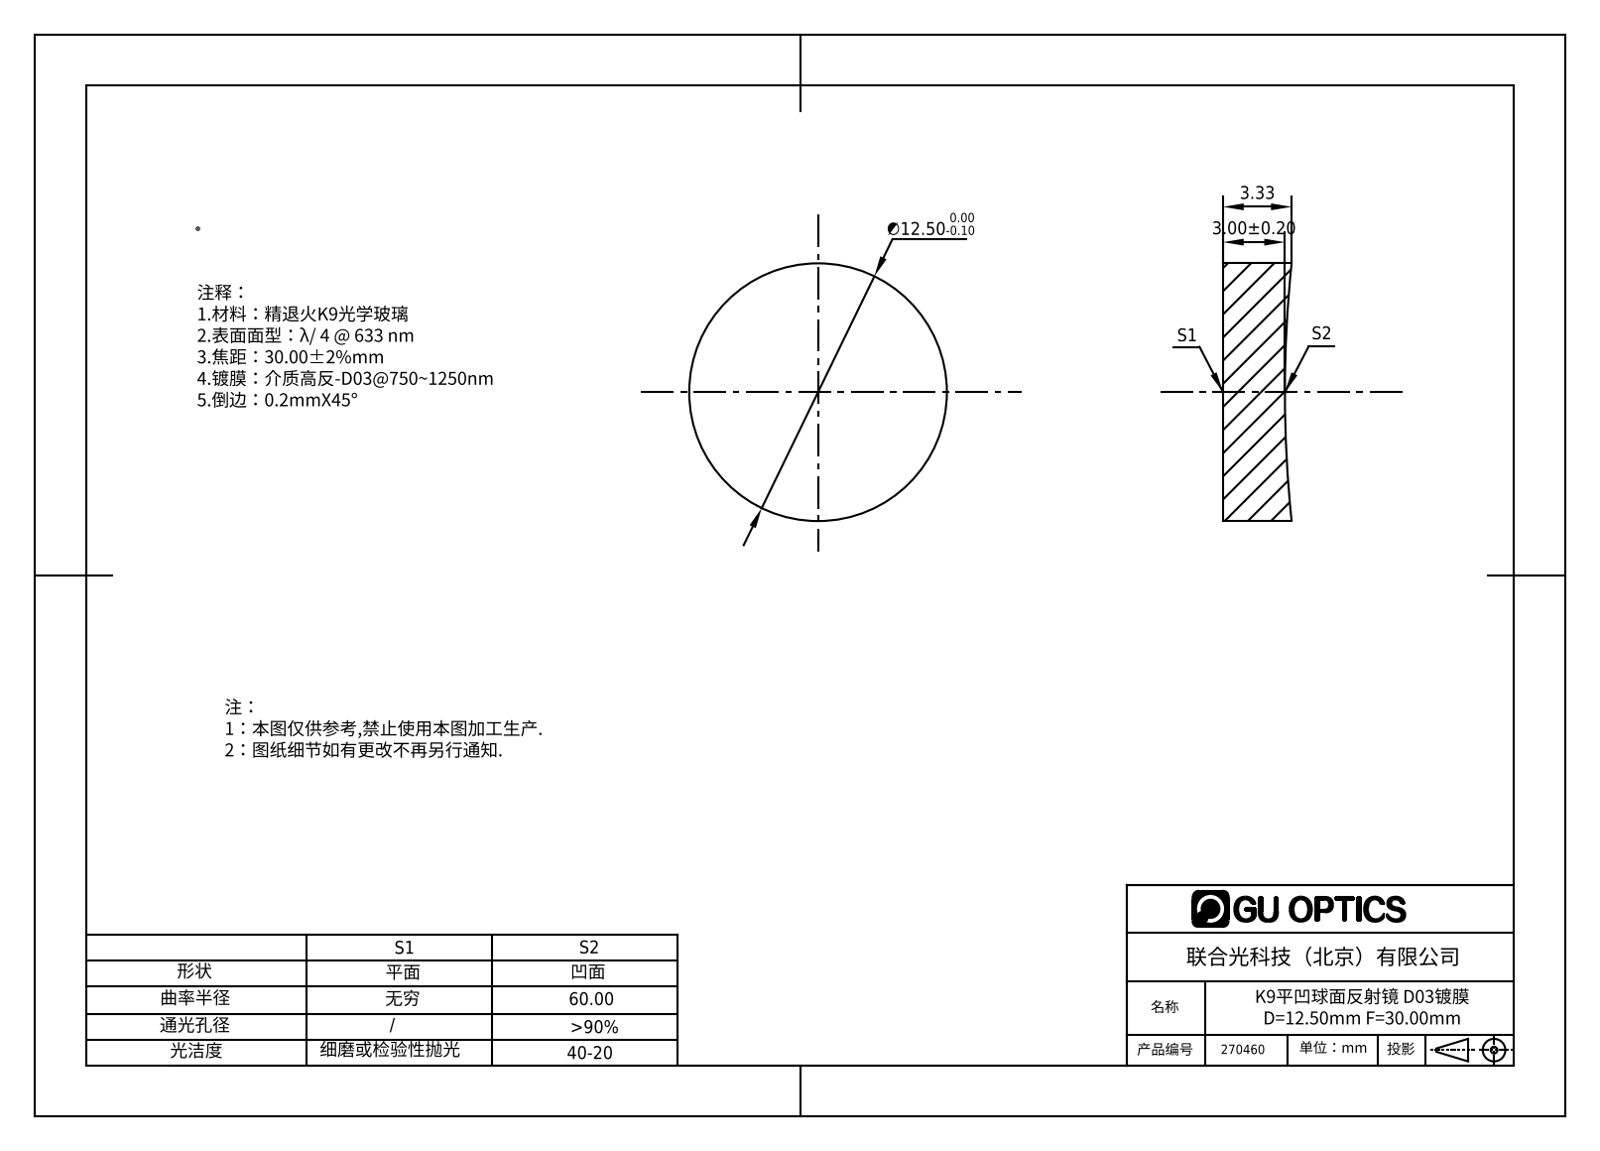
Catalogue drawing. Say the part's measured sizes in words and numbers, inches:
The part is named "270005". Its 3-D file was written by "SolidWorks 2016 (AUTOMOTIVE_DESIGN)". It is 1 solid with 5 faces: 1 planar, 2 cylindrical and 2 other. Overall it measures 0.492 by 0.492 by 0.131 inches. Its volume is 0.024 cubic inches and its surface area 0.583 square inches. Round bosses or shafts: 1 of diameter 0.492.
